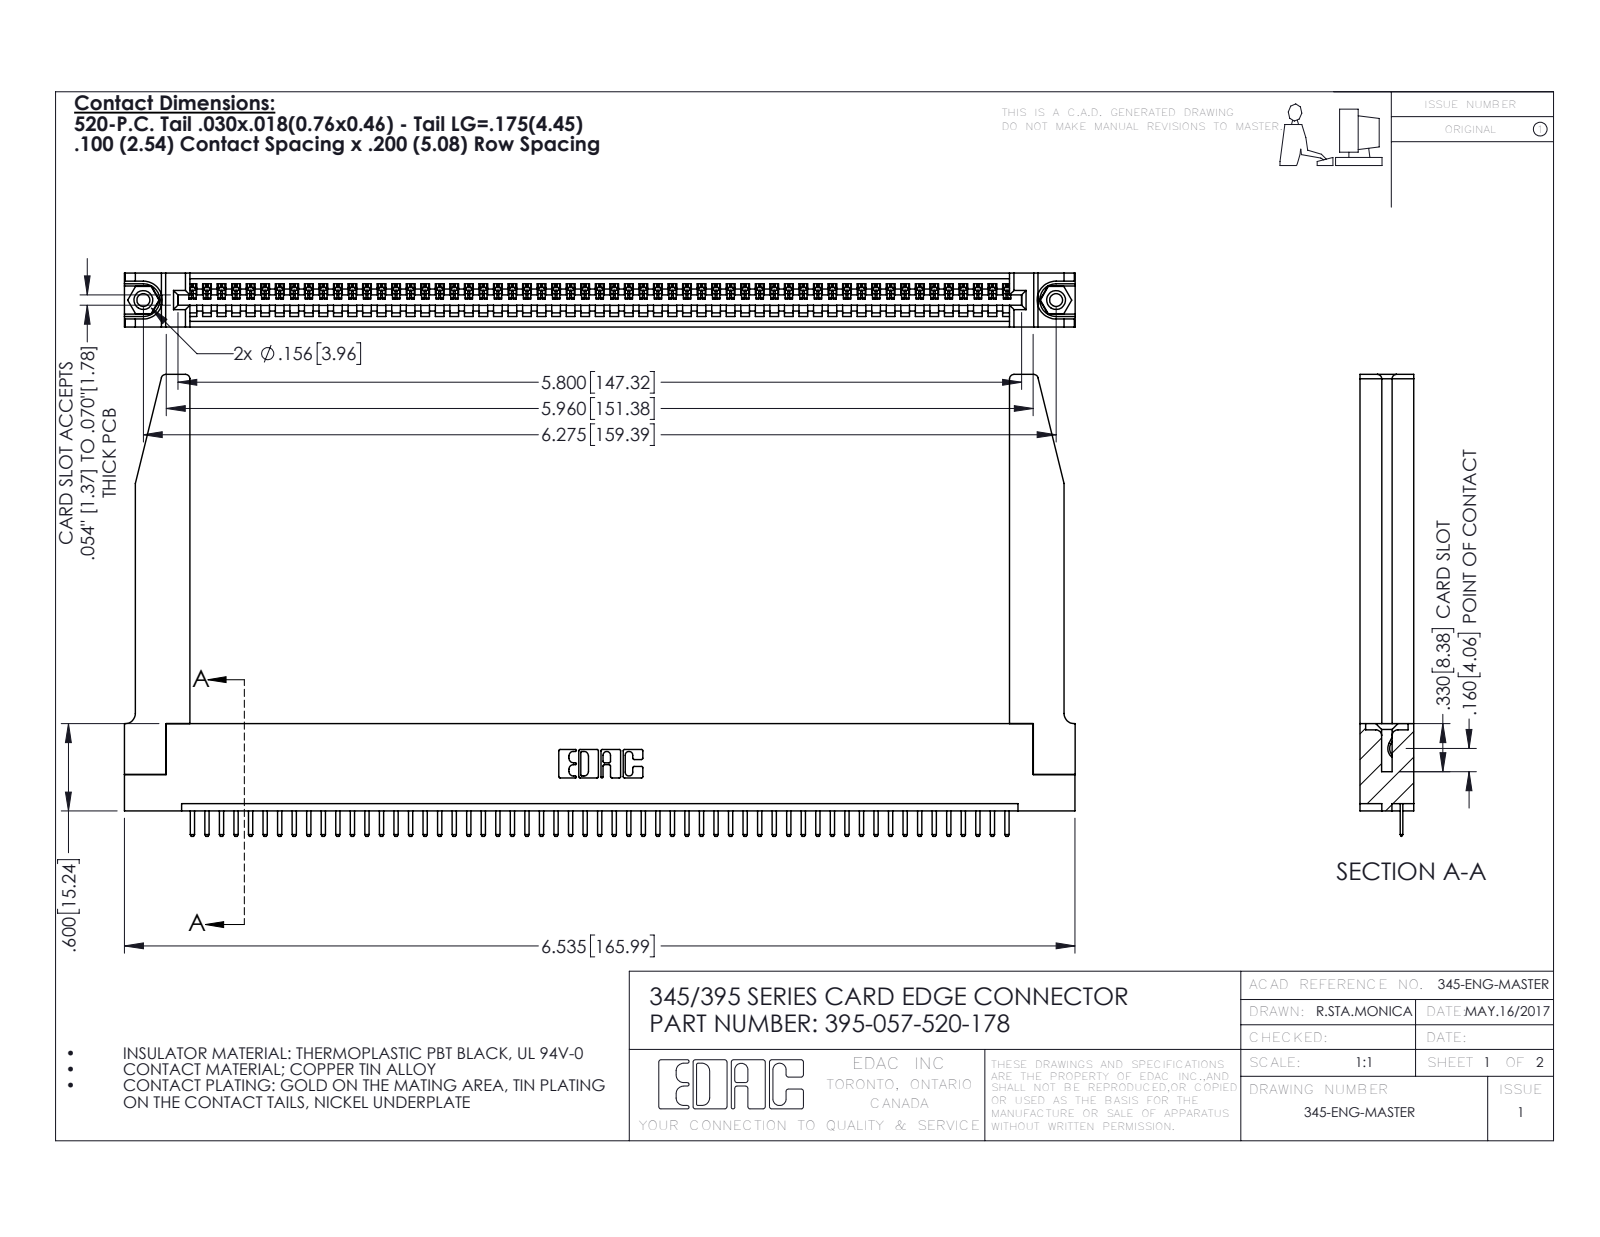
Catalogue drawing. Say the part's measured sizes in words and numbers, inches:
The part is named "345-250-001_345-250-001-102; 345-292-001_345-293-120; 345-220-078_345-220-078; 345 Part_Flush Mounting Lugs - 0.156 Dia-TH (+1 more)". Its 3-D file was written by "SolidWorks 2016 (CONFIG_CONTROL_DESIGN)". It is 62 solids with 3894 faces: 2616 planar, 1226 cylindrical and 52 other. Overall it measures 6.536 by 3.175 by 0.37 inches. Its volume is 1.434 cubic inches and its surface area 42.49 square inches. Round holes: 2 of diameter 0.089, 2 of diameter 0.125, 2 of diameter 0.156, 1 of diameter 0.064. Round bosses or shafts: 2 of diameter 0.155. Partial cylindrical surfaces (rounded edges, fillets, slot ends): 116 of radius 0.01, 114 of radius 0.006, 22 of radius 0.01, 8 of radius 0.03, 6 of radius 0.007, 6 of radius 0.031, 3 of radius 0.026, 2 of radius 0.031. The main face-to-face distances are 0.37, 0.072, 0.298, 0.2, 0.098, 0.272, 0.025, 0.225, 0.072, 0.148. The hole center spacings are 0.27, 6.039, 6.275.
